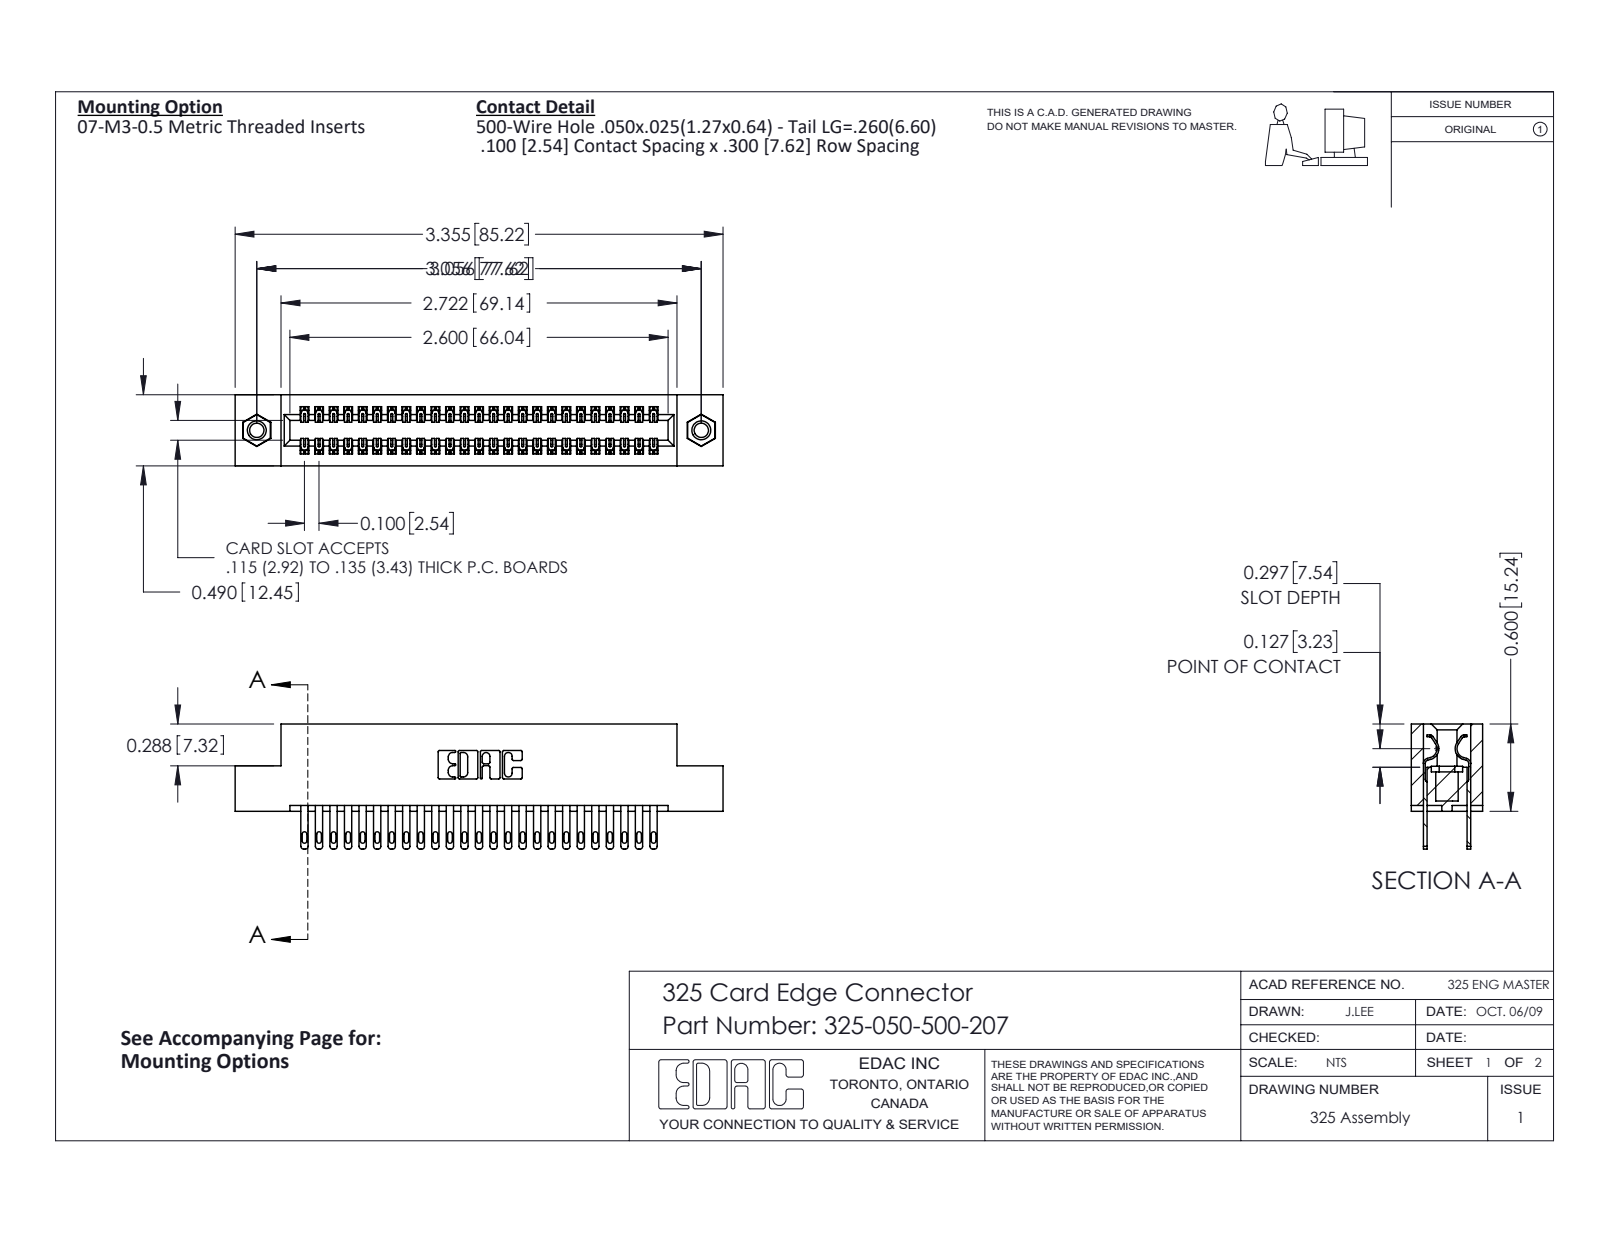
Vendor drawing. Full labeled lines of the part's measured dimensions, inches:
Part name (STEP PRODUCT): 325-292-001_325-293-100; 345-250-001_345-250-005-103; 325-050-500-207; 325 Part_TI
STEP written by: SolidWorks 2016 (CONFIG_CONTROL_DESIGN)
Units: inches
Bodies: 53 solids, 2574 faces (1602 planar, 956 cylindrical, 16 other)
Overall size (bounding box): 3.355 × 0.86 × 0.49
Volume: 0.671 in³ · Surface area: 20.84 in²
Round holes (diameter × count): ⌀0.098 ×2, ⌀0.125 ×2, ⌀0.16 ×2
Round bosses / shafts (diameter × count): ⌀0.155 ×2
Partial cylindrical surfaces — rounded edges, fillets, slot ends (radius × count): R0.006 ×75, R0.016 ×50, R0.02 ×50, R0.01 ×22, R0.007 ×6, R0.031 ×6, R0.026 ×3, R0.014 ×2
Main face-to-face distances: 0.083, 0.407, 0.3, 0.107, 0.383, 0.025, 0.49, 0.325, 0.275, 0.04
Hole centre spacings: 3.056
